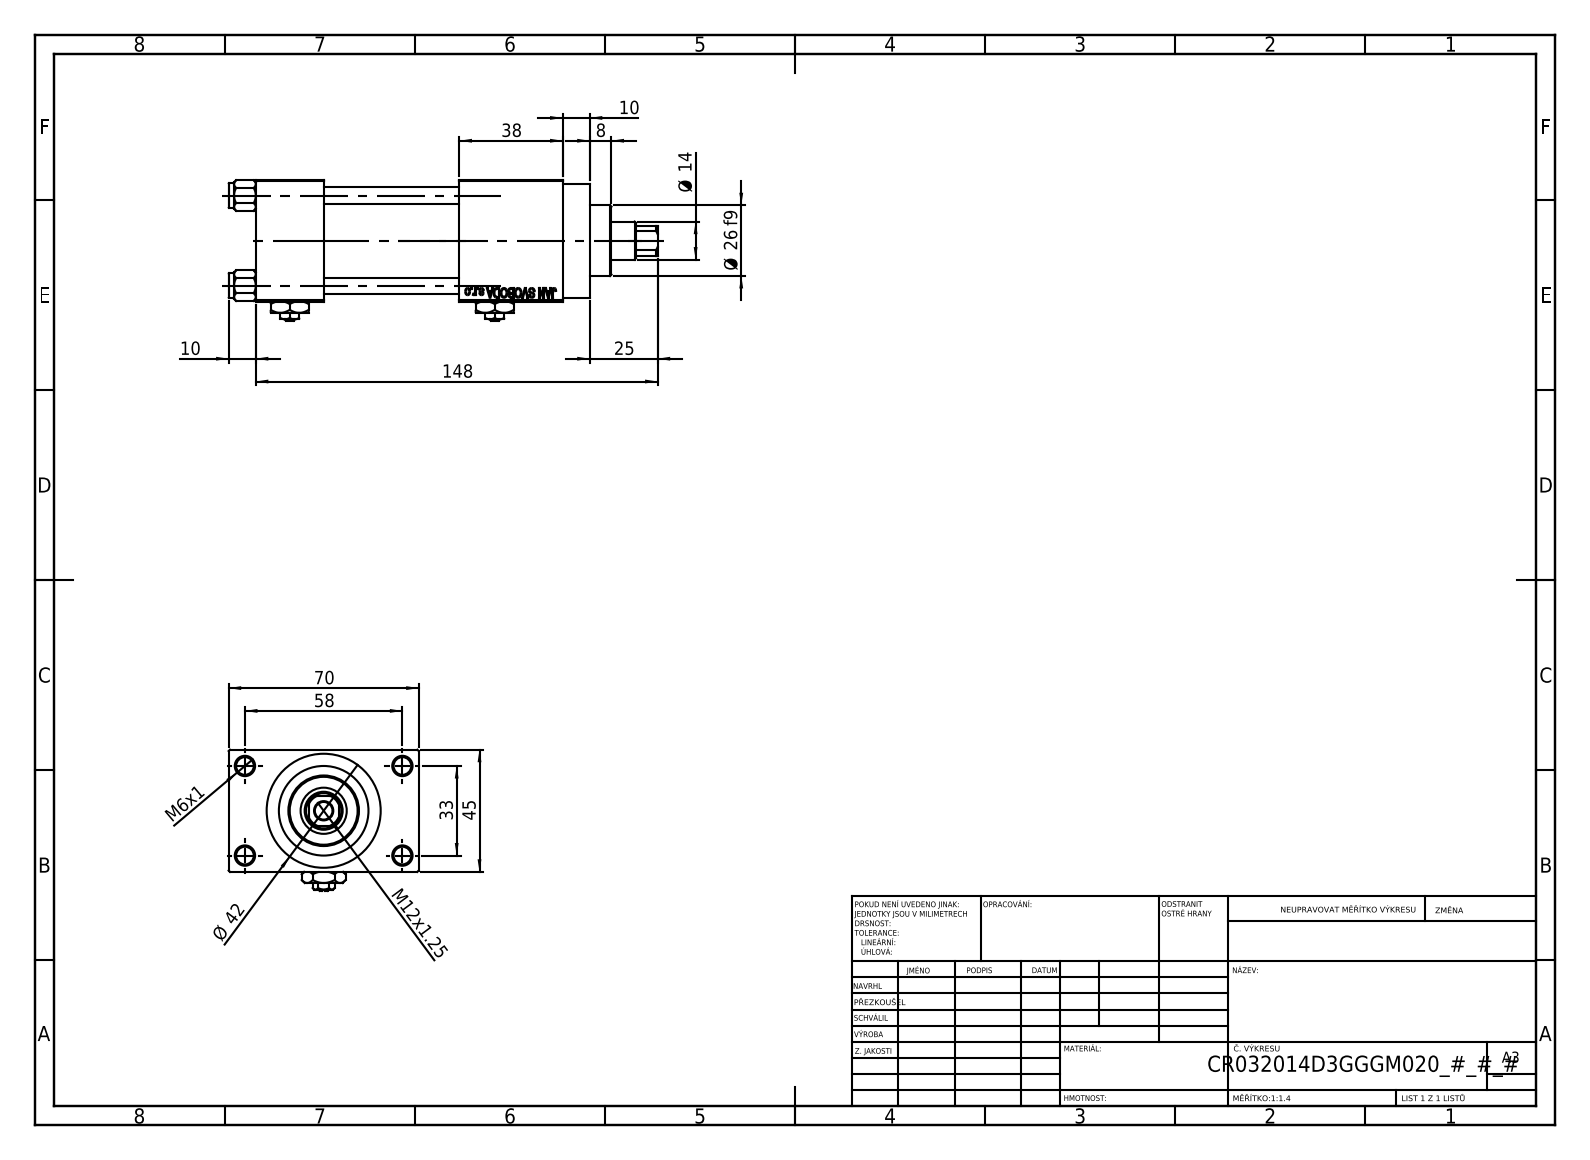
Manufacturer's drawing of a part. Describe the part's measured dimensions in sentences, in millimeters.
The part is named "Zatka_pro_OIL_PORT; V215_VC_A; V215CR_D_TYCINKA; V215CR_VCP_D (+2 more)". Its 3-D file was written by "SolidWorks 2019 (CONFIG_CONTROL_DESIGN)". It is 13 solids with 1202 faces: 542 planar, 100 cylindrical and 560 other. Overall it measures 158 by 70 by 52 millimeters. Its volume is 230 698 cubic millimeters and its surface area 76 617 square millimeters. Round holes: 5 of diameter 6.5, 4 of diameter 6, 2 of diameter 7, 2 of diameter 13.16, 2 of diameter 20, 1 of diameter 14, 1 of diameter 17, 1 of diameter 24, 1 of diameter 32, 1 of diameter 33. Round bosses or shafts: 4 of diameter 9, 1 of diameter 42, 1 of diameter 38, 1 of diameter 26. Partial cylindrical surfaces (rounded edges, fillets, slot ends): 1 of radius 6.5. The main face-to-face distances are 45, 25, 12.5, 57.5, 50, 75, 88, 70, 38, 113. The hole center spacings are 12.4, 23.48, 33.2, 33.37, 35.35, 45.6, 56.35, 33.
